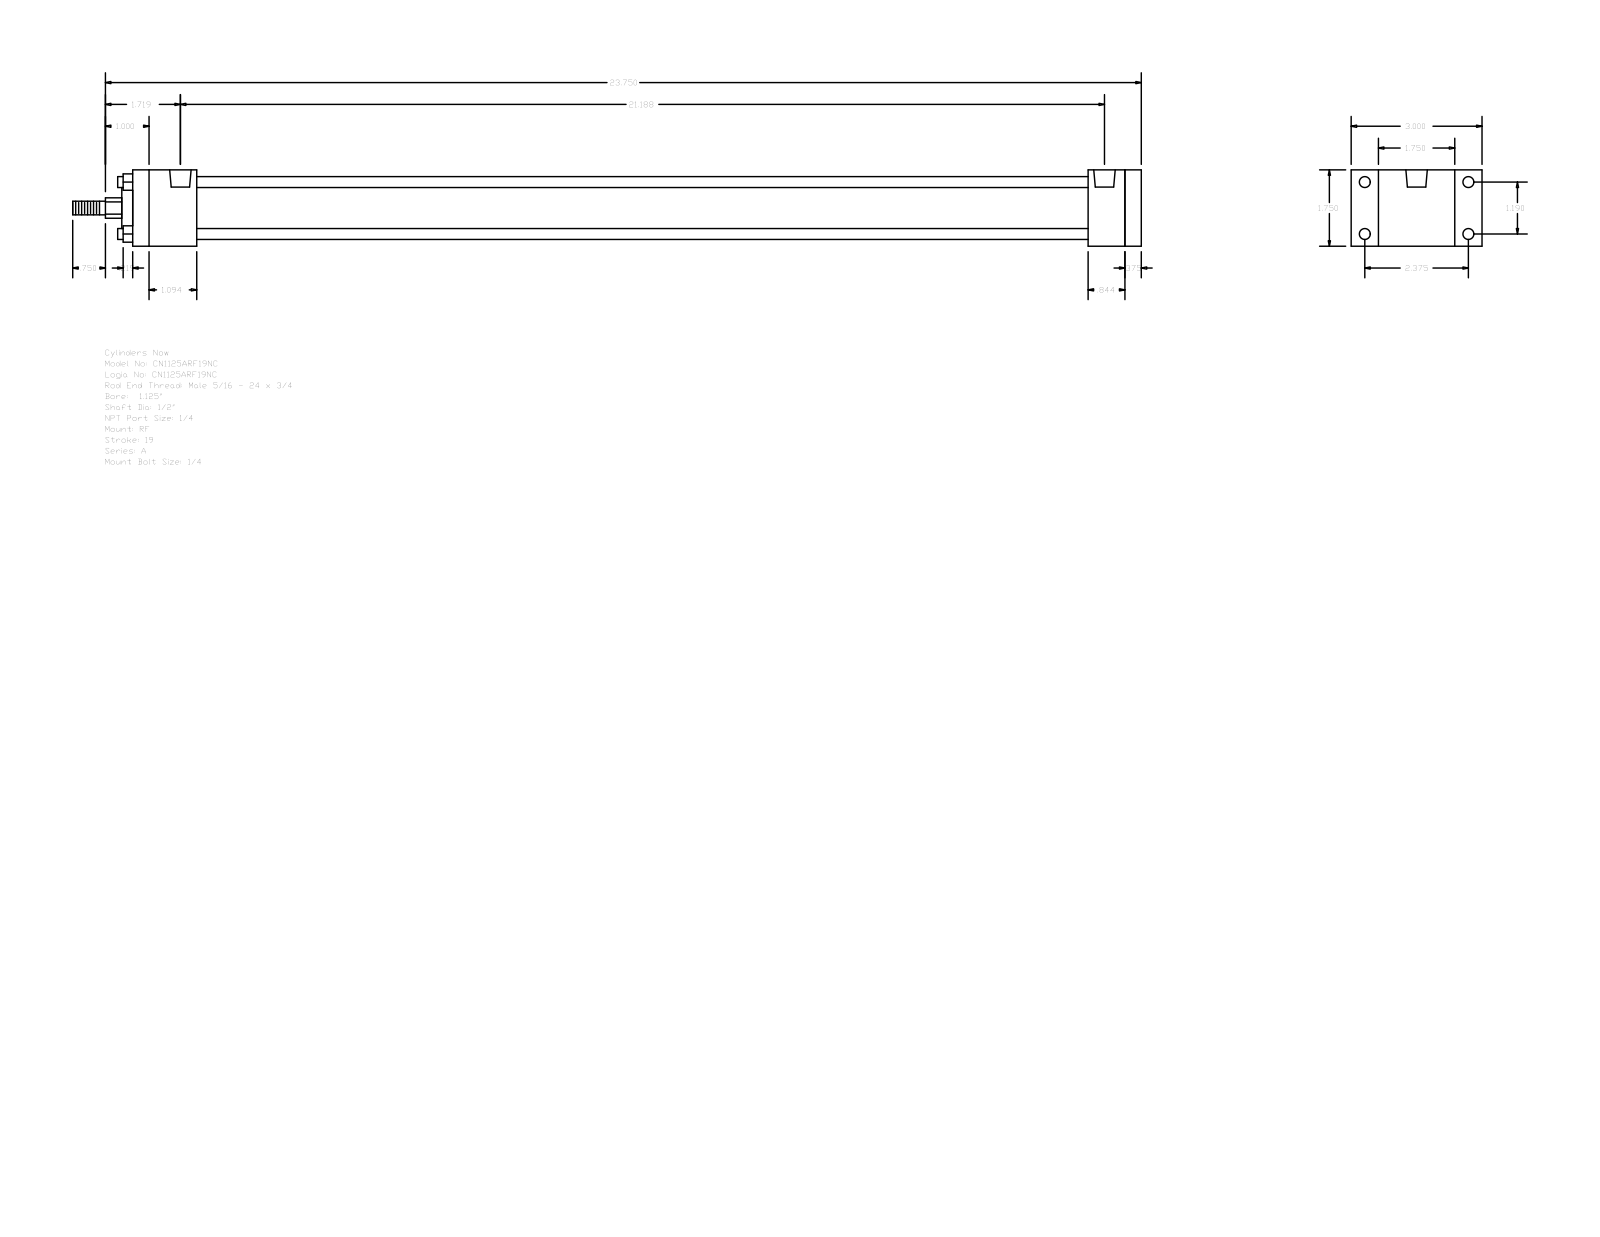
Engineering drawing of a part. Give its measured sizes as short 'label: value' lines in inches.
name: A_RF__0112_0.5
written by: GSSL Pune (CONFIG_CONTROL_DESIGN)
unit: in
bodies: 0 solids, 92 faces (64 planar, 28 cylindrical, 0 other)
size: 24.5 × 3 × 1.75
holes: 4× ⌀0.219, 4× ⌀0.25, 2× ⌀0.492
bosses: 4× ⌀0.25, 1× ⌀1.255, 1× ⌀0.937, 1× ⌀0.5, 1× ⌀0.313
rounds: 1× R0.234
face distances: 1.75, 0.375, 22.75, 23.125, 1.469, 21.906, 20.437, 21.281, 21.656, 0.844
hole spacings: 1.19, 2.375, 2.656, 21.063, 0.062, 0.063, 21.125, 21.125
